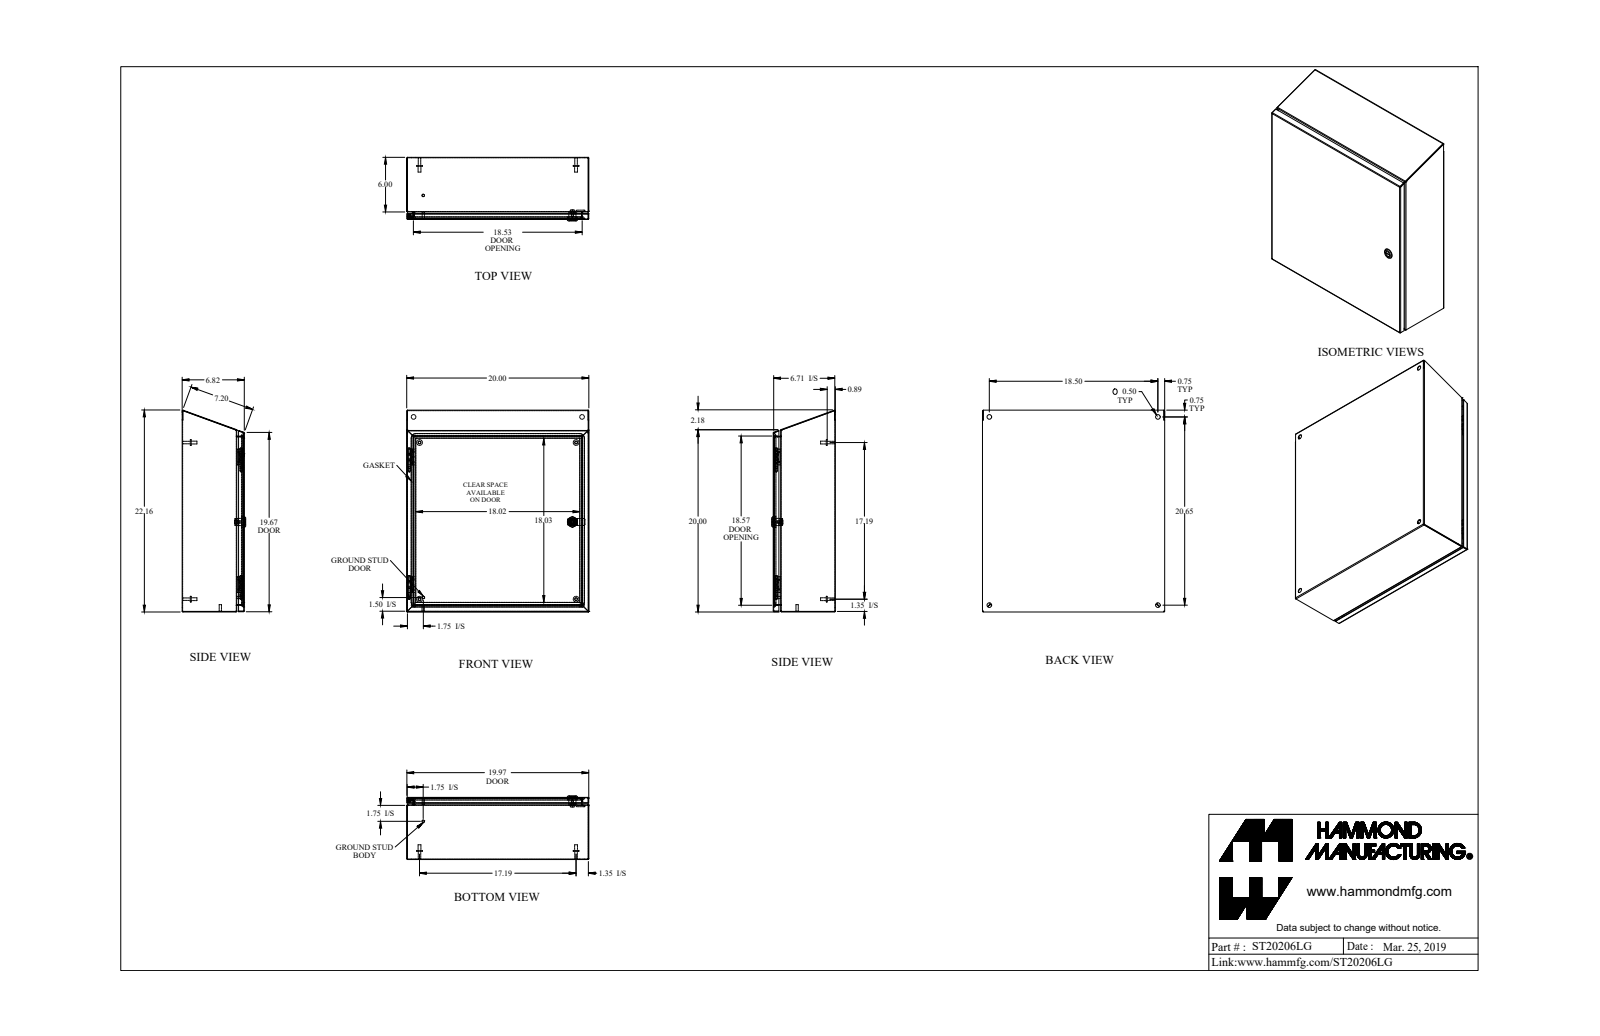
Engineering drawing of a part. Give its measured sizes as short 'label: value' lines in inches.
name: ST20206LG
written by: SolidWorks 2018 (AUTOMOTIVE_DESIGN)
unit: in
bodies: 21 solids, 632 faces (303 planar, 197 cylindrical, 132 other)
size: 22.147 × 20 × 6.982
volume: 93.02 in³; area: 3 164 in²
holes: 4× ⌀0.5, 1× ⌀0.172, 1× ⌀0.232, 1× ⌀0.24, 1× ⌀0.242, 1× ⌀0.625, 1× ⌀0.785
bosses: 4× ⌀0.625, 4× ⌀0.313, 4× ⌀0.27, 2× ⌀0.281, 2× ⌀0.25, 1× ⌀1.1, 1× ⌀0.525, 1× ⌀0.455
rounds: 21× R0.029, 21× R0.086, 11× R0.25, 4× R0.006, 4× R0.062, 4× R0.499, 2× R0.125, 1× R0.021
face distances: 0.057, 6.765, 6.708, 6.822, 19.943, 19.886, 20, 5.943, 0.822, 6
hole spacings: 18.5, 20.646, 27.722, 9.189, 11.567, 19.685, 20.902
